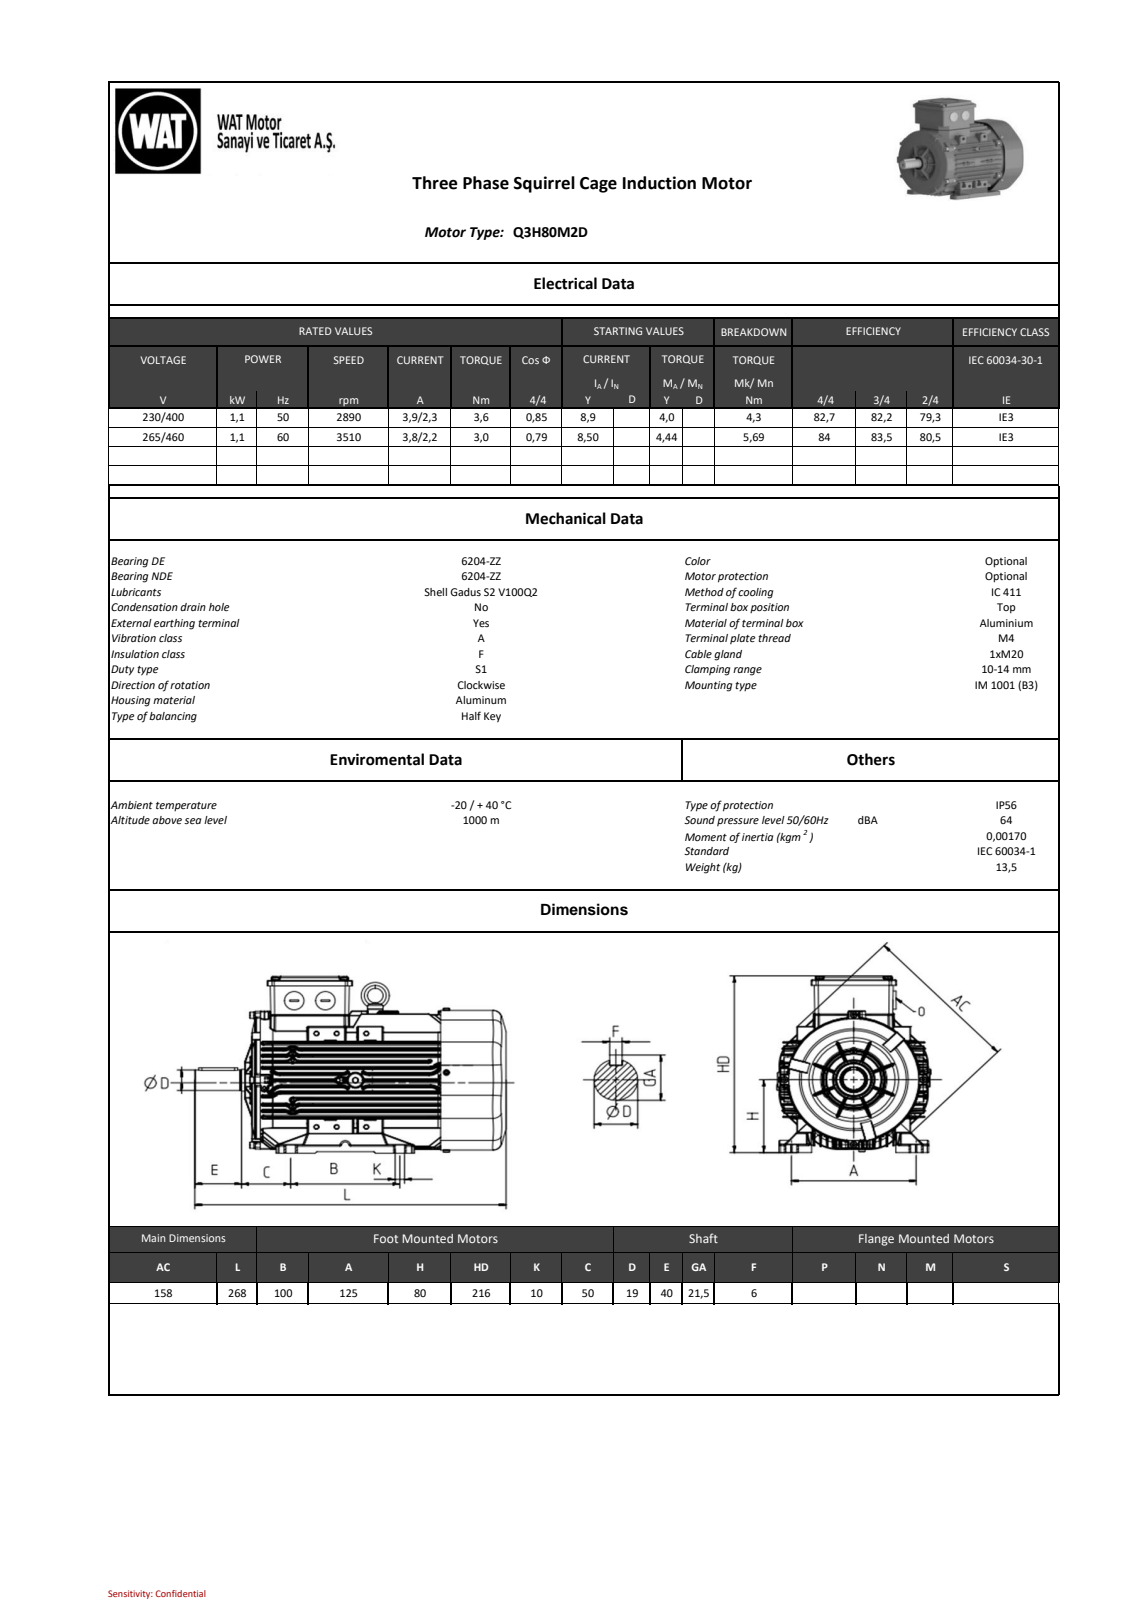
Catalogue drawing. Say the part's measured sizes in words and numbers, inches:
The part is named "QH series_ 80_B3_stp_objects". Its 3-D file was written by "SIEMENS PLM Software NX2206.8101 (AP203_CONFIGURATION_CONTROLLED_3D_DESIGN_OF_MECHANICAL_PARTS_AND_ASSEMBLIES_MIM_LF)". It is 0 solids with 6002 faces: 1266 planar, 2463 cylindrical and 2273 other. Overall it measures 10.551 by 8.484 by 6.22 inches. Round holes: 2 of diameter 0.181, 1 of diameter 0.197, 1 of diameter 0.315, 1 of diameter 2.244. Round bosses or shafts: 8 of diameter 0.236, 4 of diameter 0.328, 2 of diameter 0.842, 1 of diameter 5.768, 1 of diameter 2.402, 1 of diameter 0.948, 1 of diameter 0.795, 1 of diameter 0.787. Partial cylindrical surfaces (rounded edges, fillets, slot ends): 640 of radius 0.039, 578 of radius 0.02, 441 of radius 0.031, 71 of radius 0.079, 26 of radius 0.197, 12 of radius 0.02, 8 of radius 0.315, 6 of radius 0.118. The main face-to-face distances are 0.039, 6.181, 1.652, 0.408, 6.18, 3.386, 0.709, 0.826, 0.413, 0.276. The hole center spacings are 2.793.
